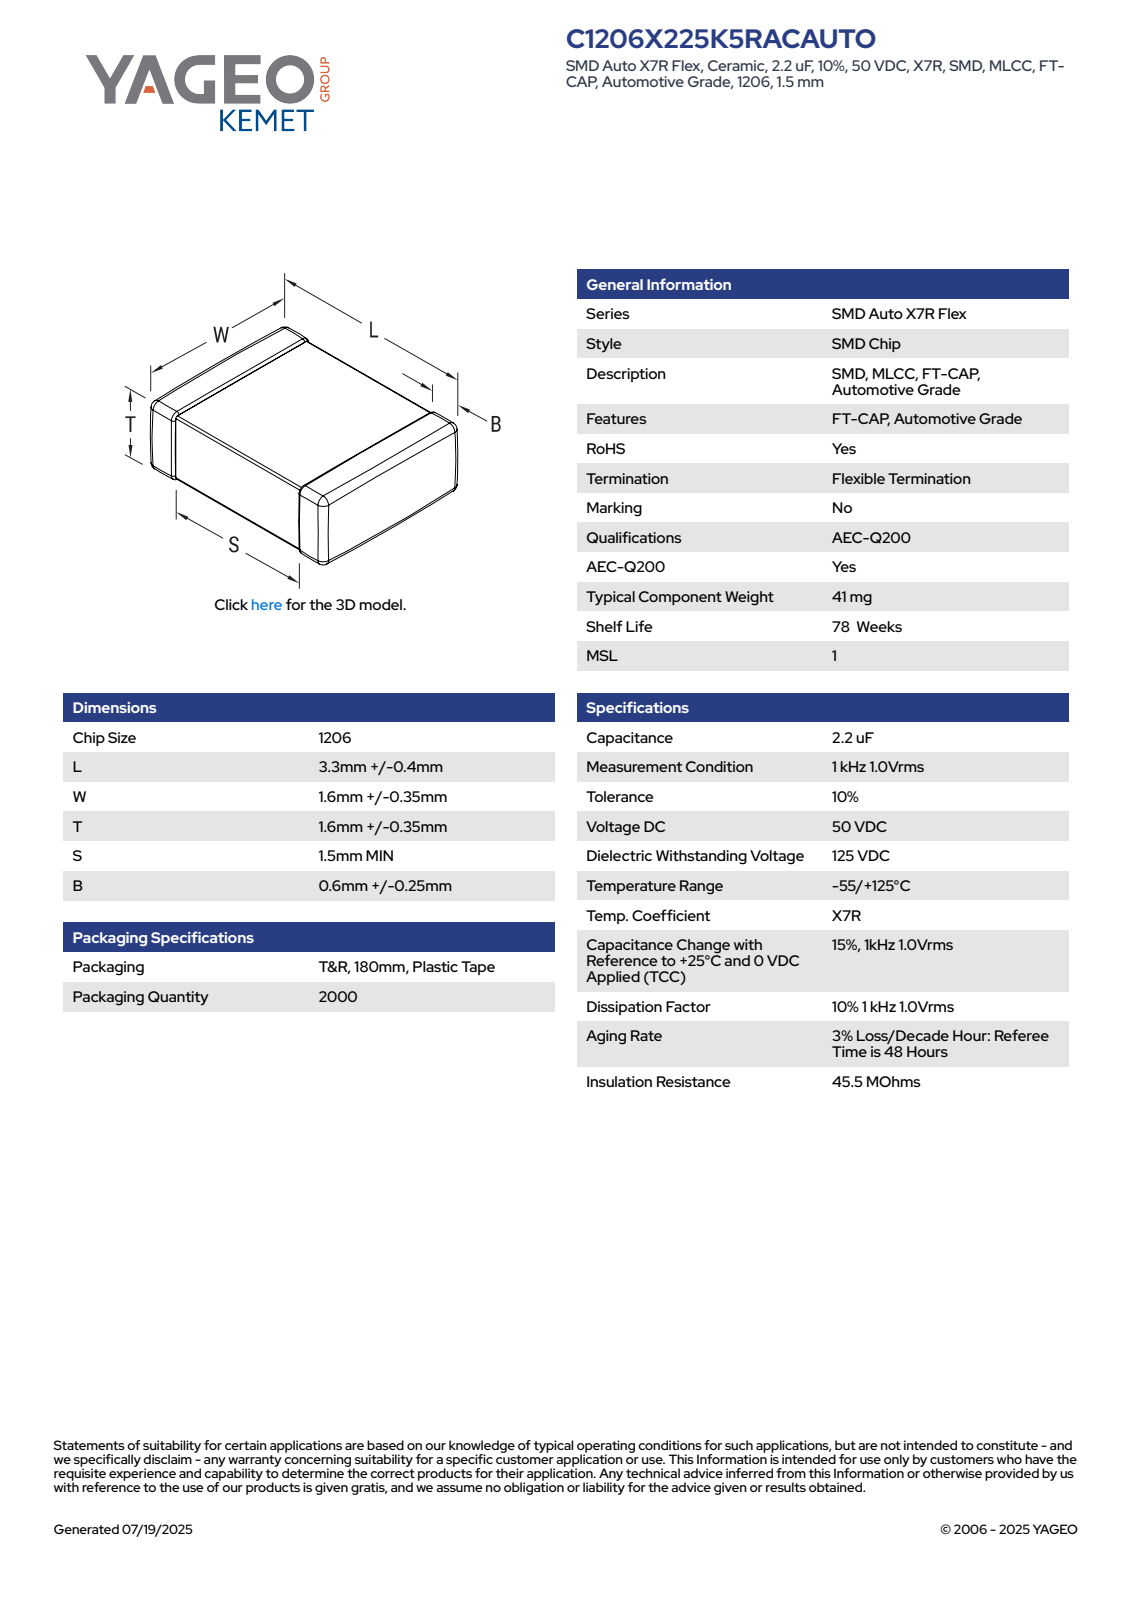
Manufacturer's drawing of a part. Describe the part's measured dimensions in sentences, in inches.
The part is named "CCS_CCSTDNOS_1206_L3.7W1.95T1.8B0.85". Its 3-D file was written by "SolidWorks 2014 (AUTOMOTIVE_DESIGN)". It is 4 solids with 125 faces: 71 planar, 38 cylindrical and 16 other. Overall it measures 0.146 by 0.077 by 0.071 inches. Its volume is 0.001 cubic inches and its surface area 0.053 square inches. The main face-to-face distances are 0.069, 0.075, 0.068, 0.074, 0.146, 0.071, 0.077, 0.034, 0.032, 0.041.
